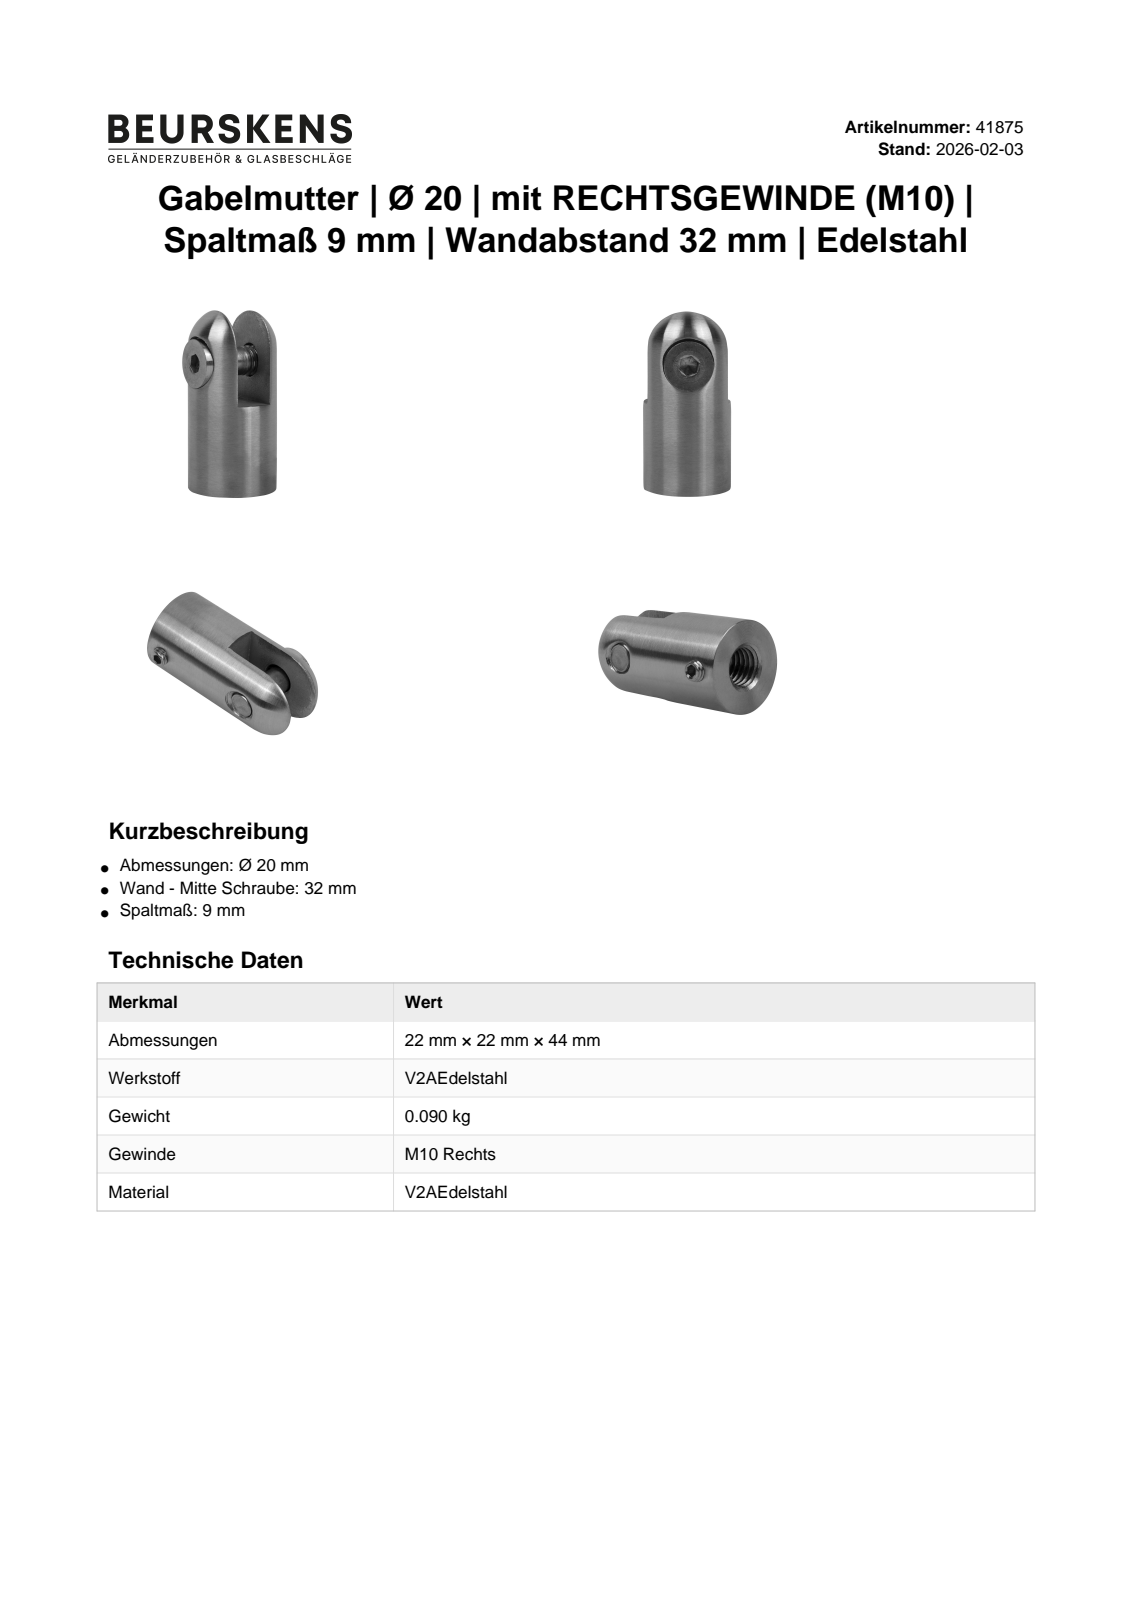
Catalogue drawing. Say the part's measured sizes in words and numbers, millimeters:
The part is named "41875". Its 3-D file was written by "Autodesk Inventor 2022 (AUTOMOTIVE_DESIGN)". It is 1 solid with 15 faces: 6 planar, 6 cylindrical and 3 other. Overall it measures 43.54 by 22 by 22 millimeters. Its volume is 9 637 cubic millimeters and its surface area 4 517 square millimeters. Round holes: 1 of diameter 5, 1 of diameter 8, 1 of diameter 10, 1 of diameter 12.5. Round bosses or shafts: 1 of diameter 22. The main face-to-face distances are 9, 22, 15, 7, 13, 4. The hole center spacings are 27.
